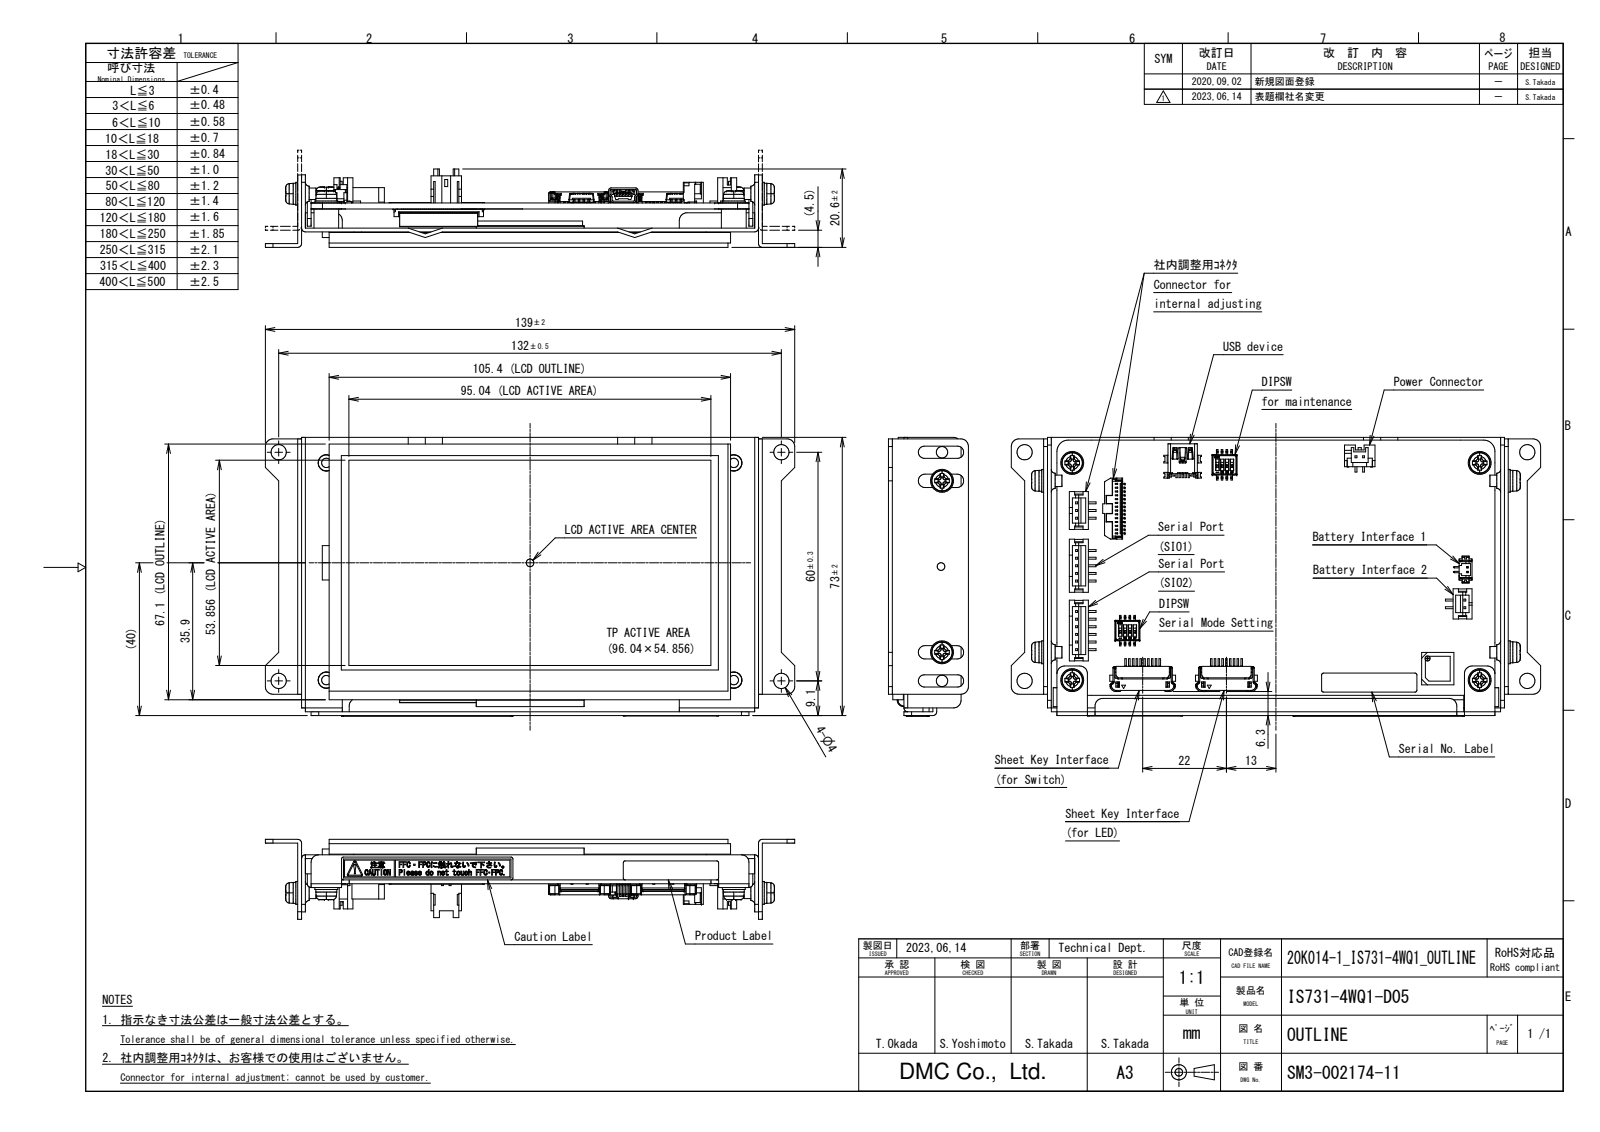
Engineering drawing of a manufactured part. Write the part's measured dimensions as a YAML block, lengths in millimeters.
part_name: "HP_IS731-4WQ1-D05"
step_written_by: "Autodesk Inventor 2020 (AUTOMOTIVE_DESIGN)"
units: millimeters
bodies: {solids: 1, faces: 5526, planar: 4084, cylindrical: 805, other: 637}
overall_size: [139, 73.2, 21]
volume: 60613
surface_area: 58171
round_holes:
  - {diameter: 4, count: 6}
  - {diameter: 2.46, count: 4}
  - {diameter: 3.5, count: 4}
  - {diameter: 4.25, count: 4}
  - {diameter: 1.2, count: 2}
  - {diameter: 0.3, count: 1}
  - {diameter: 1.33, count: 1}
  - {diameter: 2, count: 1}
round_bosses_or_shafts:
  - {diameter: 3, count: 8}
  - {diameter: 6, count: 6}
  - {diameter: 5.5, count: 6}
  - {diameter: 8, count: 4}
  - {diameter: 6.5, count: 4}
  - {diameter: 4.24, count: 4}
partial_cylinders:
  - {radius: 0.1, count: 116}
  - {radius: 0.2, count: 50}
  - {radius: 0.3, count: 48}
  - {radius: 0.15, count: 29}
  - {radius: 2, count: 20}
  - {radius: 0.13, count: 16}
  - {radius: 0.4, count: 15}
  - {radius: 0.5, count: 13}
face_to_face_distances: [6.6, 11.66, 1.6, 5.06, 1, 5, 10.06, 4.06, 7.6, 6]
hole_center_spacings: [12.5, 12.81, 57, 58.55, 60, 61.09, 107, 119.5]
